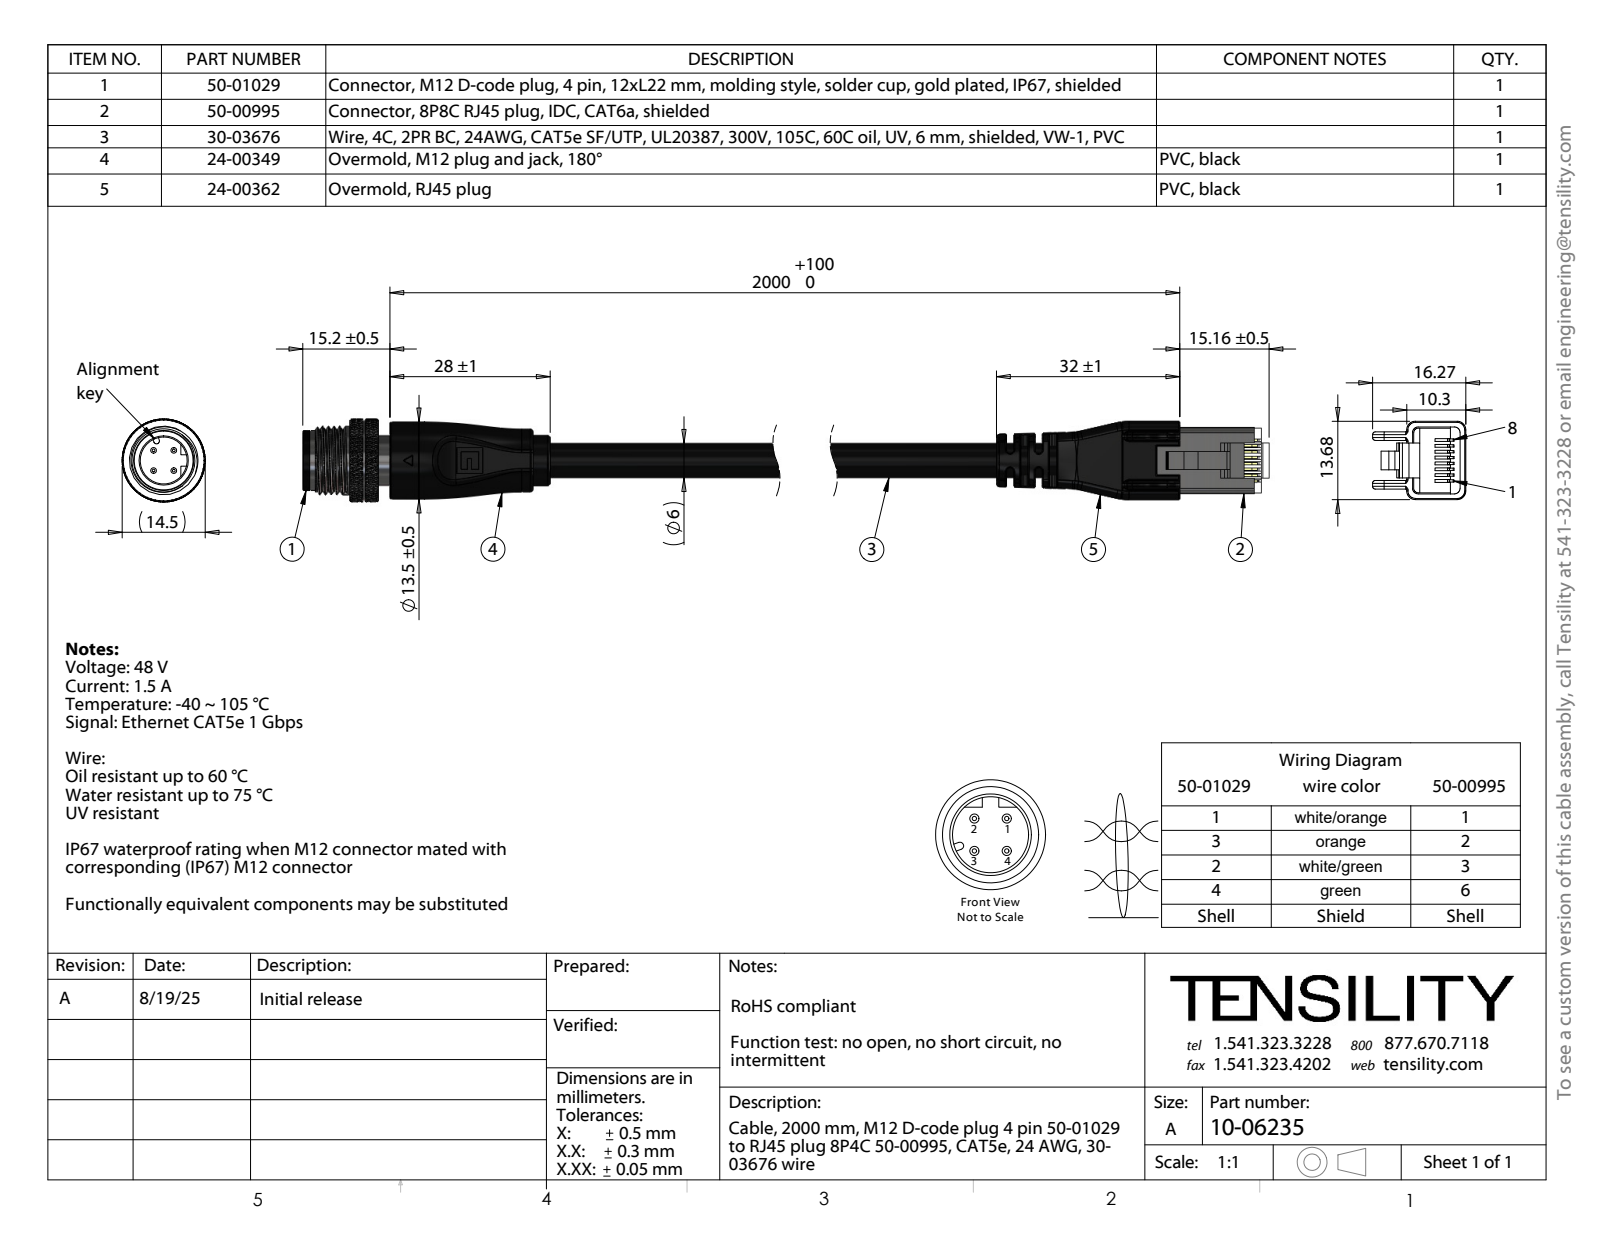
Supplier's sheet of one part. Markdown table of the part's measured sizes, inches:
| quantity | value |
| --- | --- |
| part name | 10-06235; 30-03676_blunt cut; 50-01029-03_默认; 50-01029-04_默认 (+6 more) |
| STEP written by | SolidWorks 2025 (CONFIG_CONTROL_DESIGN) |
| units | inches |
| bodies | 54 solids, 3209 faces (470 planar, 811 cylindrical, 1928 other) |
| overall size | 9.067 × 0.723 × 0.571 |
| volume | 0.849 in³ |
| surface area | 45.15 in² |
| round holes (diameter × count) | 0.008 × 28, 0.039 × 4, 0.041 × 4, 0.124 × 1, 0.126 × 1, 0.14 × 1, 0.315 × 1, 0.323 × 1, 0.346 × 1, 0.374 × 1 |
| round bosses / shafts (diameter × count) | 0.055 × 4, 0.571 × 1, 0.547 × 1, 0.531 × 1, 0.472 × 1, 0.433 × 1, 0.413 × 1, 0.366 × 1 |
| partial cylindrical surfaces (radius × count) | 0.008 × 11, 0.02 × 10, 0.059 × 10, 0.024 × 8, 0.039 × 5, 0.394 × 4, 0.031 × 2, 0.045 × 2 |
| main face-to-face distances | 0.049, 0.098, 0.039, 0.148, 0.197, 0.366, 0.276, 7.854, 0.499, 0.46 |
| hole center spacings | 0.042, 0.075, 0.082, 0.014, 0.043, 0.067, 0.071, 0.089 |
